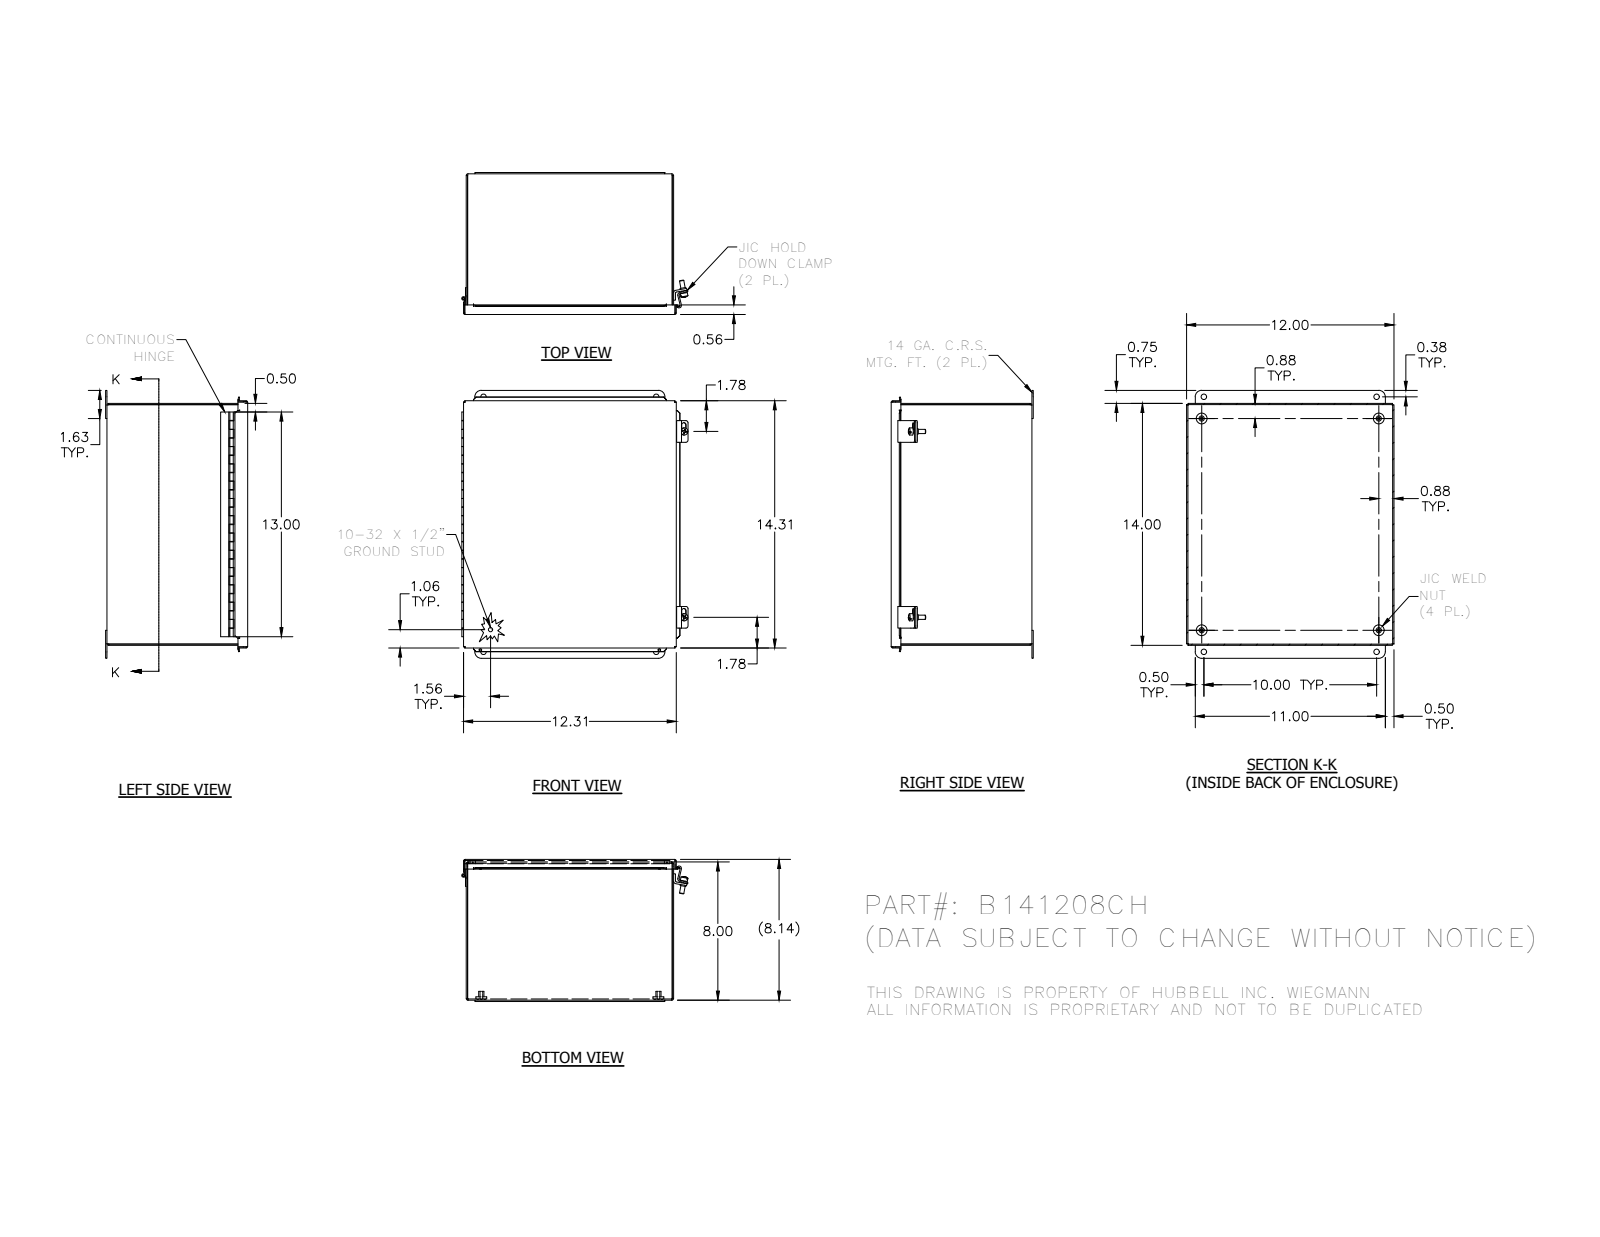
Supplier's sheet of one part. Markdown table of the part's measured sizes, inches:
| quantity | value |
| --- | --- |
| part name | B141208CH; 3499; 3485; C1001 (+8 more) |
| STEP written by | Autodesk Inventor 2012 (AUTOMOTIVE_DESIGN) |
| units | inches |
| bodies | 20 solids, 519 faces (335 planar, 139 cylindrical, 45 other) |
| overall size | 15.5 × 13.087 × 8.219 |
| volume | 67.02 in³ |
| surface area | 1 840 in² |
| round holes (diameter × count) | 0.156 × 4, 0.31 × 4, 0.14 × 2, 0.196 × 2, 0.116 × 1 |
| round bosses / shafts (diameter × count) | 0.625 × 4, 0.3 × 4, 0.25 × 3, 0.41 × 2, 0.344 × 2, 0.2 × 1, 0.19 × 1, 0.1 × 1 |
| partial cylindrical surfaces (radius × count) | 0.031 × 15, 0.105 × 8, 0.125 × 8, 0.093 × 7, 0.133 × 4, 0.375 × 4, 0.063 × 3, 0.126 × 3 |
| main face-to-face distances | 0.074, 11.926, 8.083, 13.926, 0.062, 8.144, 8.009, 8.07, 12, 11.852 |
| hole center spacings | 1.256, 10, 10.202, 10.202, 10.25, 13.501, 14.75, 16.875 |
